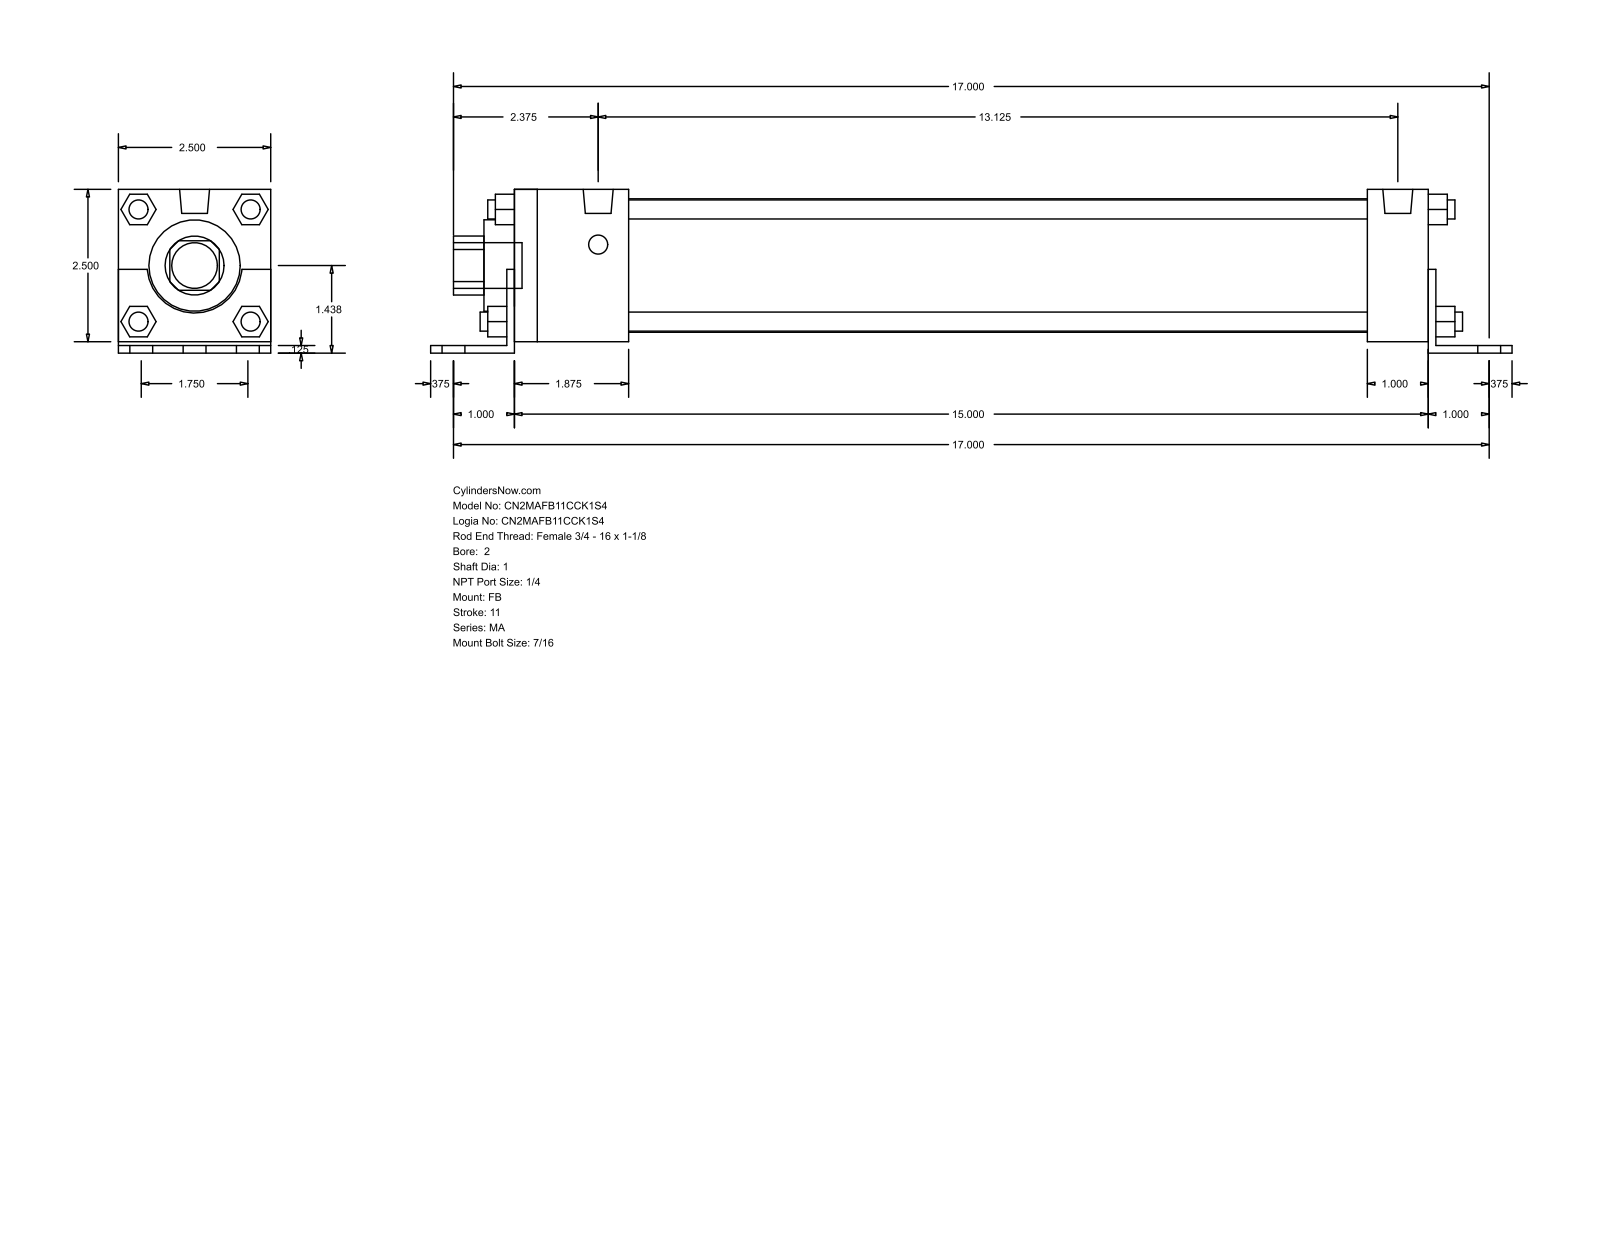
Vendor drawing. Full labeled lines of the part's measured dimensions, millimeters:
Part name (STEP PRODUCT): MA_FB__0200_1
STEP written by: GSSL Pune (CONFIG_CONTROL_DESIGN)
Units: millimetres
Bodies: 0 solids, 140 faces (105 planar, 35 cylindrical, 0 other)
Overall size (bounding box): 450.85 × 68.26 × 63.5
Round holes (diameter × count): ⌀25.4 ×1, ⌀38.1 ×1, ⌀55.63 ×1
Round bosses / shafts (diameter × count): ⌀7.94 ×8, ⌀11.11 ×6, ⌀12.49 ×2, ⌀19.05 ×1
Partial cylindrical surfaces — rounded edges, fillets, slot ends (radius × count): R12.29 ×1, R19.81 ×1
Main face-to-face distances: 63.5, 3.17, 4.76, 68.26, 1.59, 65.09, 384.17, 12.7, 381, 25.4
